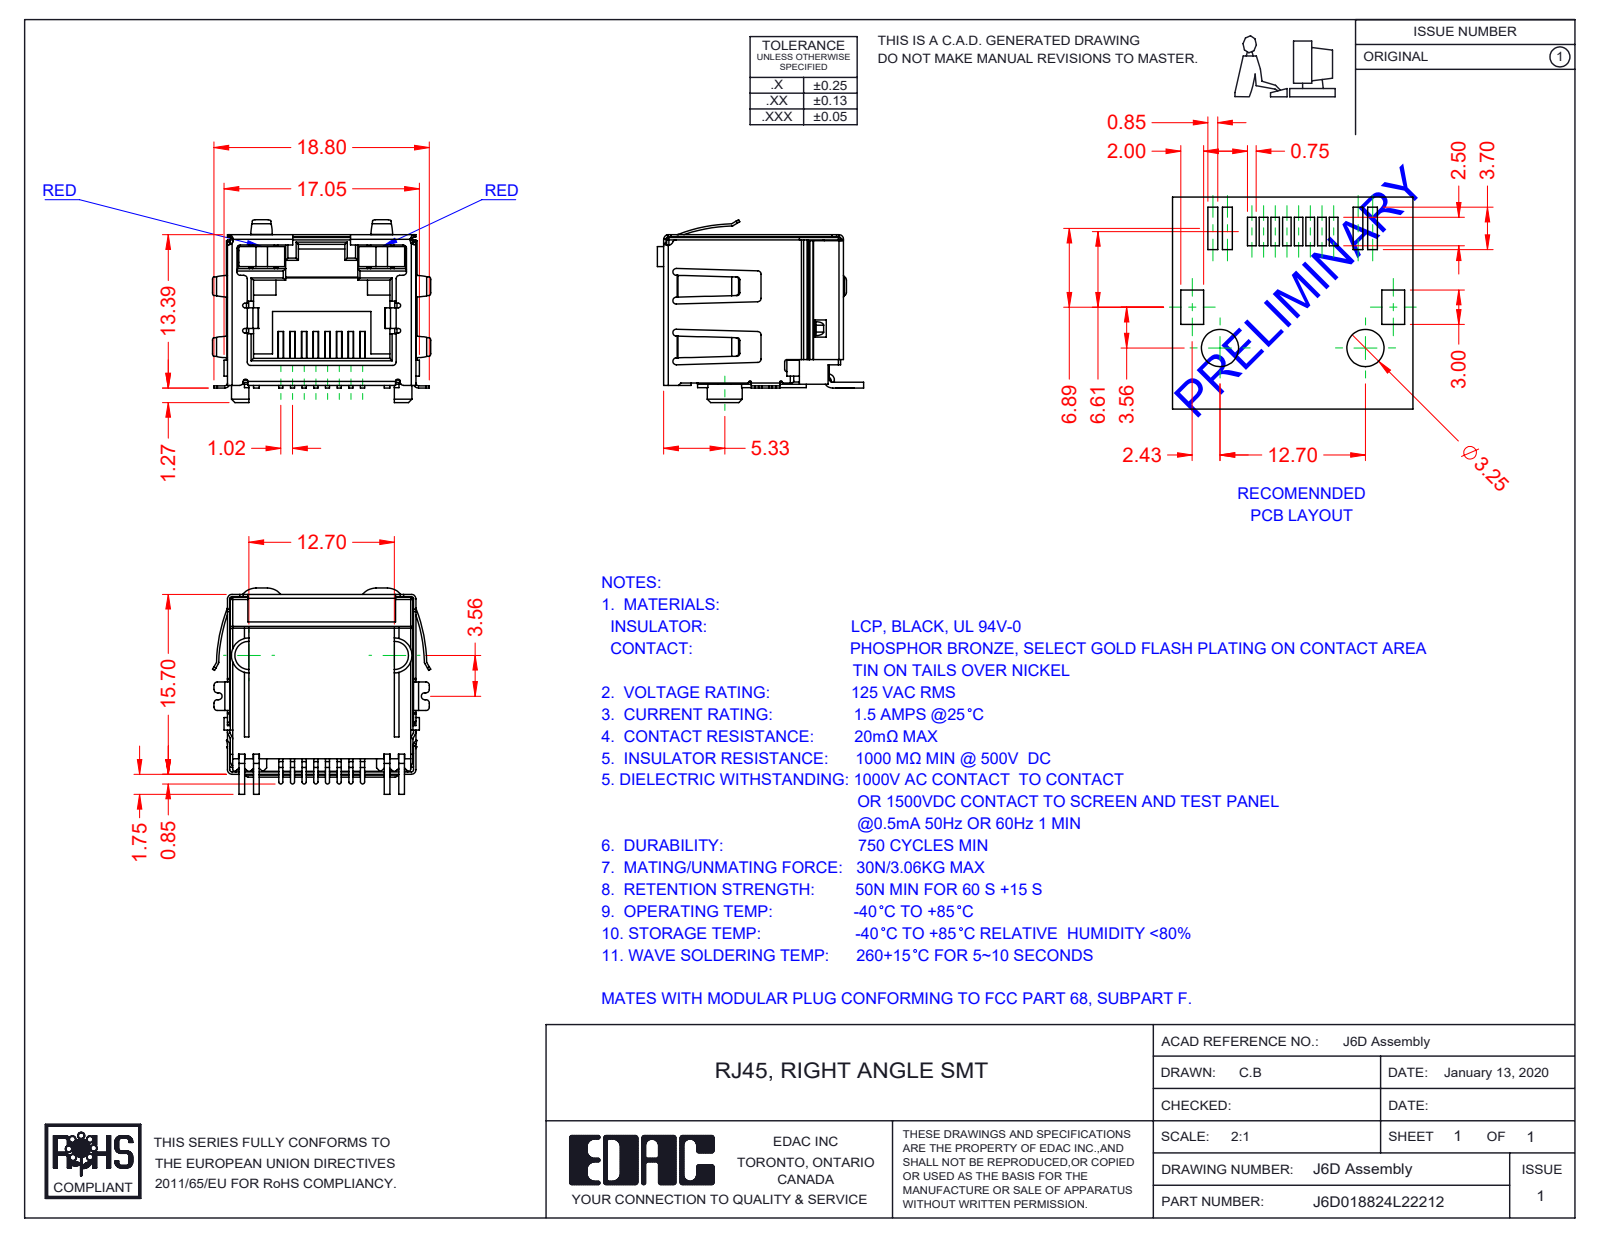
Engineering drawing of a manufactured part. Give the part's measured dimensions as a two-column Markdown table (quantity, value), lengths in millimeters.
| quantity | value |
| --- | --- |
| part name | 6D LED LH_2-Red; J6D018824L22212; 6D LED RH_2-Red; 6D Shield_LED - EMI (+2 more) |
| STEP written by | SolidWorks 2016 (CONFIG_CONTROL_DESIGN) |
| units | millimeters |
| bodies | 12 solids, 1028 faces (701 planar, 282 cylindrical, 45 other) |
| overall size | 19.06 × 18 × 15.95 |
| volume | 1 790 mm³ |
| surface area | 4 796 mm² |
| partial cylindrical surfaces (radius × count) | 0.3 × 55, 0.2 × 40, 0.4 × 19, 0.25 × 16, 0.1 × 12, 0.15 × 8, 0.18 × 8, 0.5 × 6 |
| main face-to-face distances | 16, 16.2, 16.25, 2.25, 1, 15.95, 12.8, 0.45, 13.05, 10.6 |
